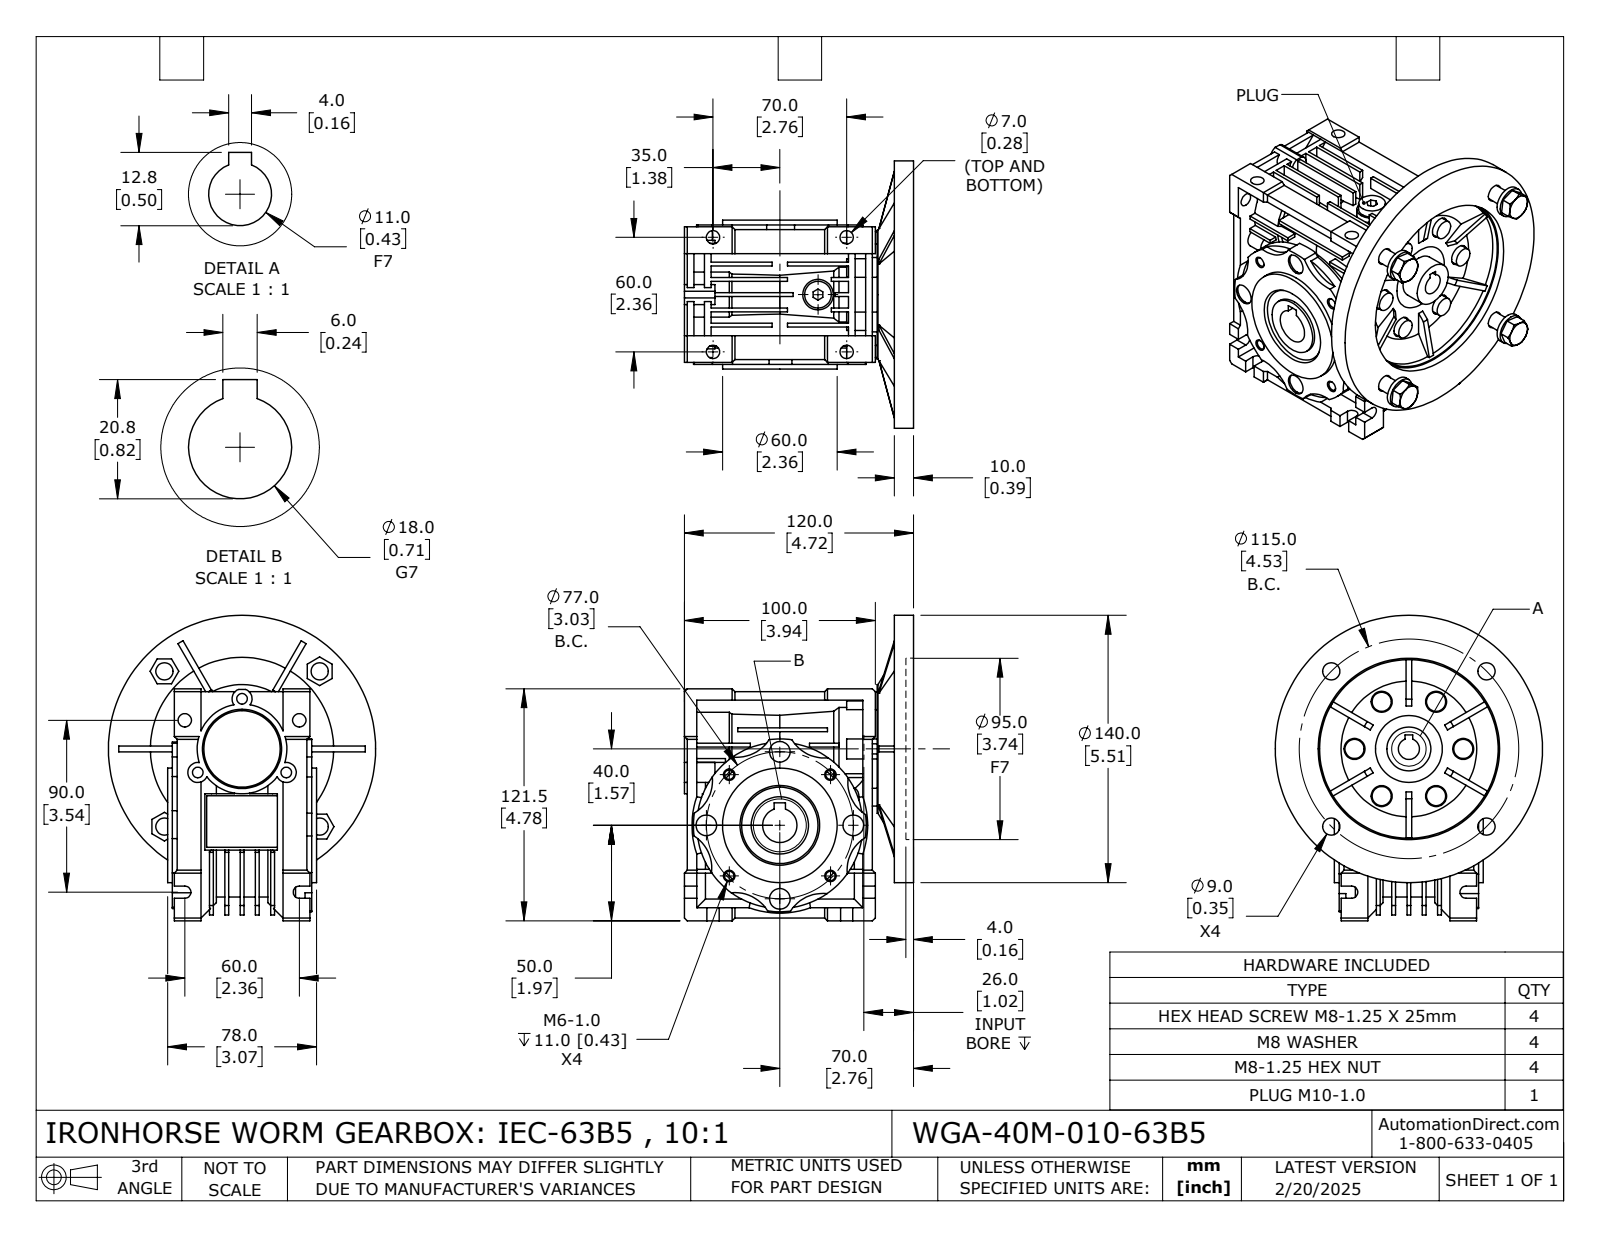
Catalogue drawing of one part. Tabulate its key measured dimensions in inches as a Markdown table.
| quantity | value |
| --- | --- |
| part name | WGA-40M-010-63B5 |
| STEP written by | SolidWorks 2024 (CONFIG_CONTROL_DESIGN) |
| units | inches |
| bodies | 18 solids, 1083 faces (592 planar, 298 cylindrical, 193 other) |
| overall size | 6.299 × 5.512 × 5.432 |
| volume | 45.77 in³ |
| surface area | 295.5 in² |
| round holes (diameter × count) | 0.433 × 7, 0.276 × 6, 0.354 × 5, 0.194 × 4, 0.268 × 4, 0.315 × 4, 0.359 × 4, 0.425 × 4, 0.219 × 3, 0.453 × 1, 0.709 × 1, 0.906 × 1 |
| round bosses / shafts (diameter × count) | 0.394 × 6, 0.63 × 5, 5.512 × 1, 2.953 × 1, 2.657 × 1, 2.362 × 1, 2.126 × 1, 1.85 × 1 |
| partial cylindrical surfaces (radius × count) | 0.787 × 8, 0.126 × 6, 0.206 × 6, 0.207 × 3, 1.713 × 1, 1.716 × 1, 1.781 × 1, 1.811 × 1 |
| main face-to-face distances | 0.394, 0.315, 0.236, 0.079, 0.197, 0.059, 0.63, 0.945, 0.551, 0.098 |
| hole center spacings | 1.122, 1.146, 2.765, 1.943, 1.215, 1.32, 1.476, 1.516 |
